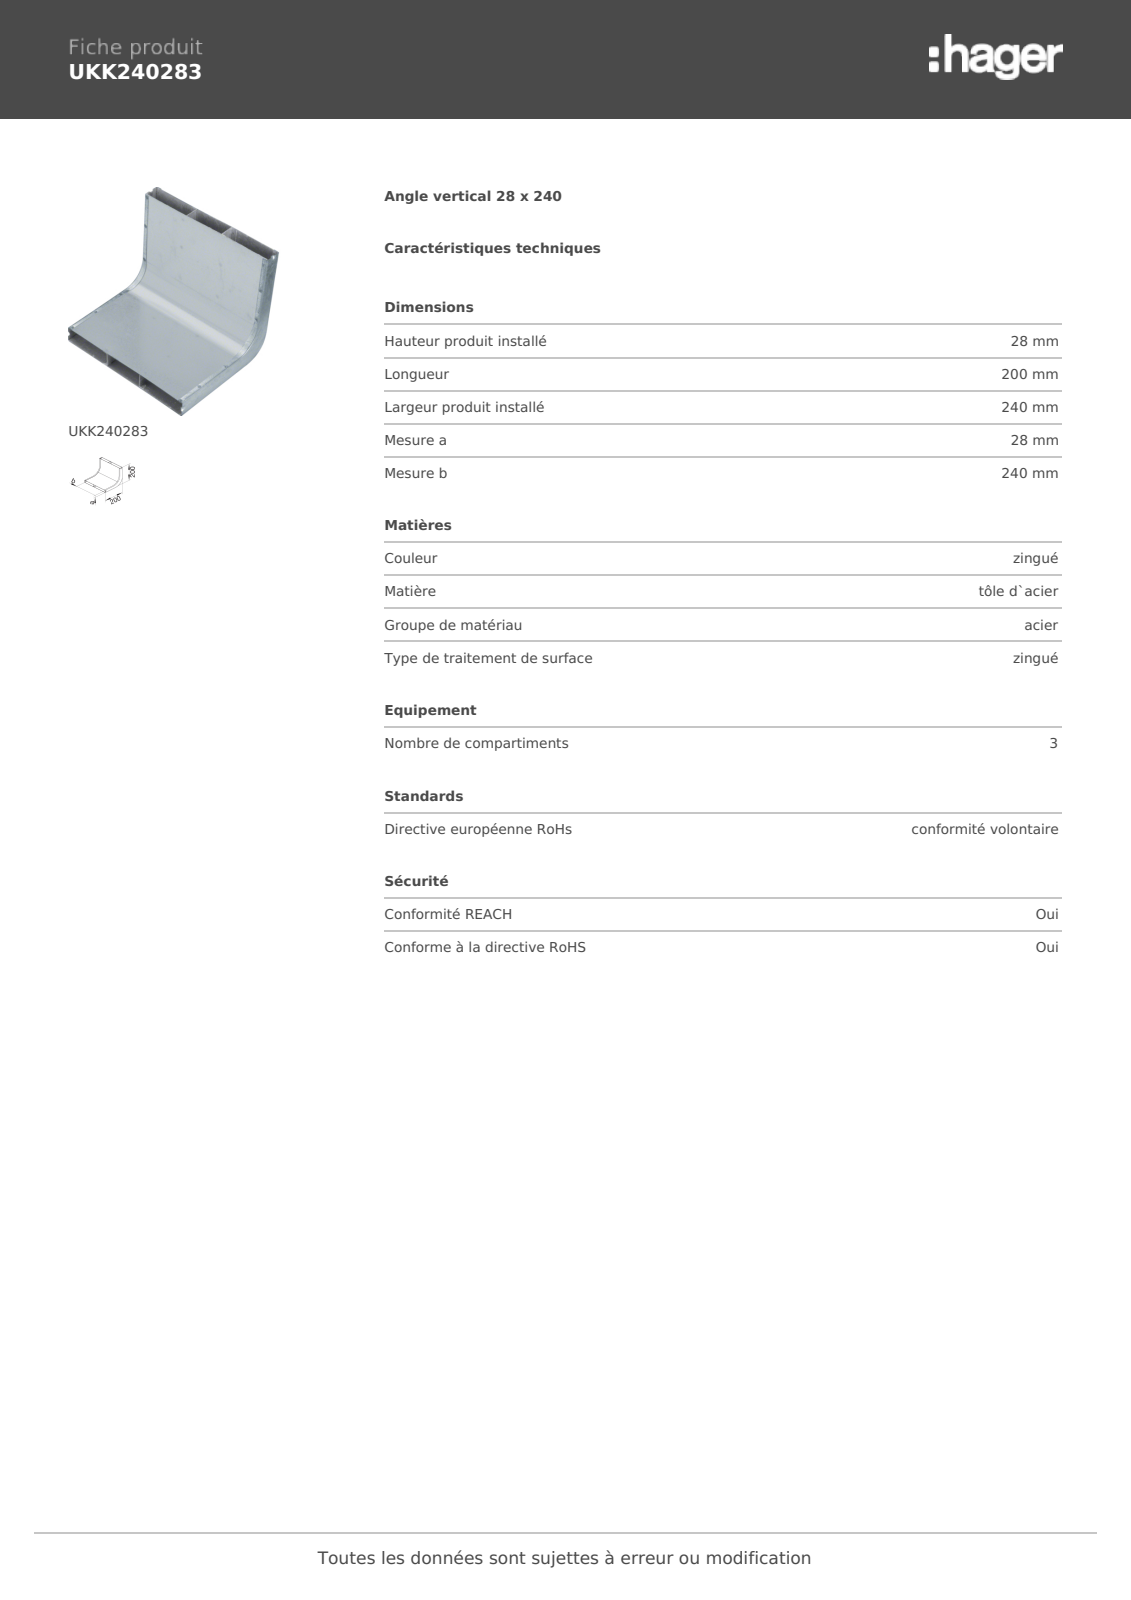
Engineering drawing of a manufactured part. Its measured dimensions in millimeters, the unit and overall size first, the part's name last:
Units: millimetres
Overall size (bounding box): 240 × 200.53 × 200.5
Partial cylindrical surfaces — rounded edges, fillets, slot ends (radius × count): R1 ×5, R1.75 ×3, R0.25 ×1
Main face-to-face distances: 0.75, 25.75, 25, 26.5, 85.75, 153.5, 239.25, 67.75, 86.5, 154.25
Volume: 171 431 mm³ · Surface area: 461 418 mm²
Bodies: 6 solids, 76 faces (60 planar, 16 cylindrical, 0 other)
Part name (STEP PRODUCT): UKKA_240-SIMPLIFIED; UKKS_28-SIMPLIFIED; UKKT_28-SIMPLIFIED; UKKI_240-28-SIMPLIFIED (+1 more)
STEP written by: CREO PARAMETRIC BY PTC INC, 2022024 (AUTOMOTIVE_DESIGN)
